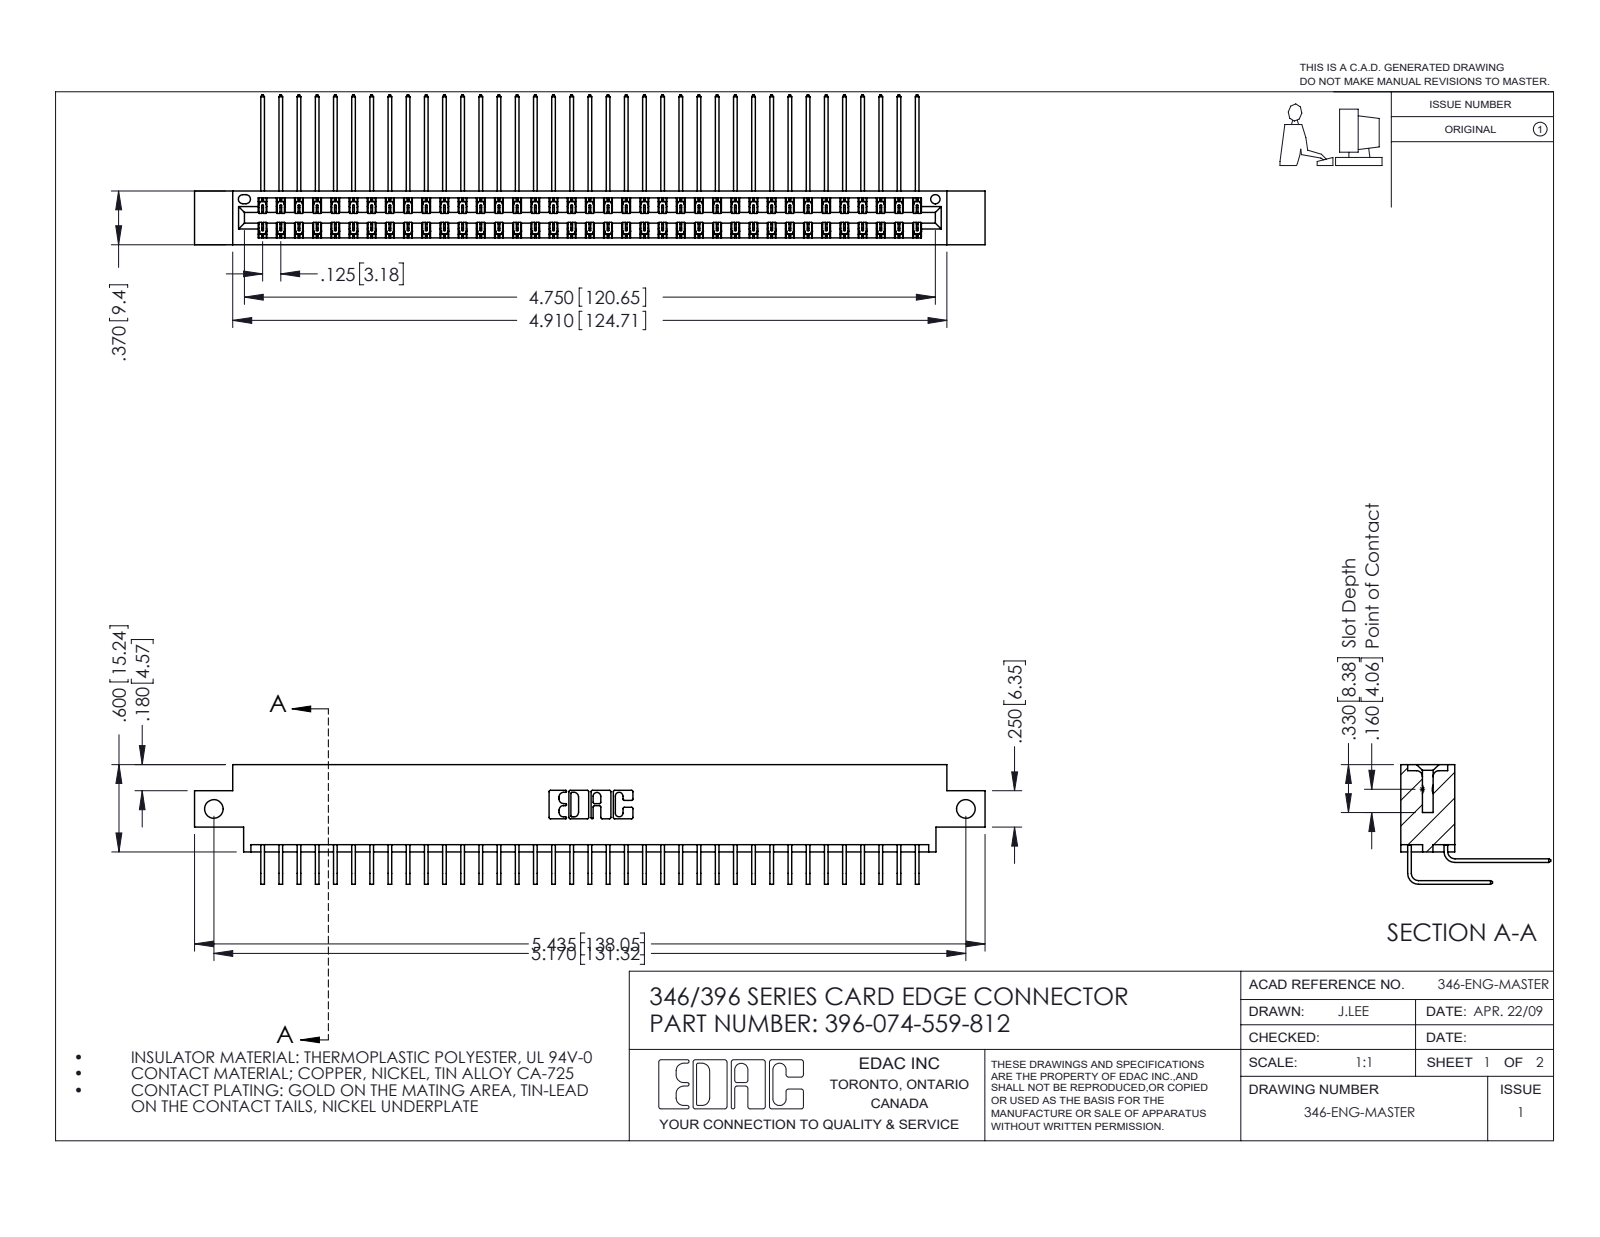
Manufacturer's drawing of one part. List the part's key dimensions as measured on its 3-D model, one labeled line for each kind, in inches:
Part name (STEP PRODUCT): 345-292-001_559 Tail - 2; 346 Part_0.170 Offset - Side Mount; 396-074-559-812; 345-292-001_558 559 Tail - 1
STEP written by: SolidWorks 2016 (CONFIG_CONTROL_DESIGN)
Units: inches
Bodies: 75 solids, 4122 faces (2818 planar, 1304 cylindrical, 0 other)
Overall size (bounding box): 5.435 × 1.03 × 0.823
Volume: 0.83 in³ · Surface area: 32.11 in²
Round holes (diameter × count): ⌀0.128 ×2, ⌀0.064 ×1
Partial cylindrical surfaces — rounded edges, fillets, slot ends (radius × count): R0.006 ×111, R0.01 ×22, R0.007 ×6, R0.031 ×6, R0.026 ×3, R0.014 ×2, R0.022 ×2, R0.024 ×2
Main face-to-face distances: 0.048, 0.322, 0.025, 0.37, 0.25, 0.072, 0.298, 0.275, 0.148, 0.222
Hole centre spacings: 5.17
